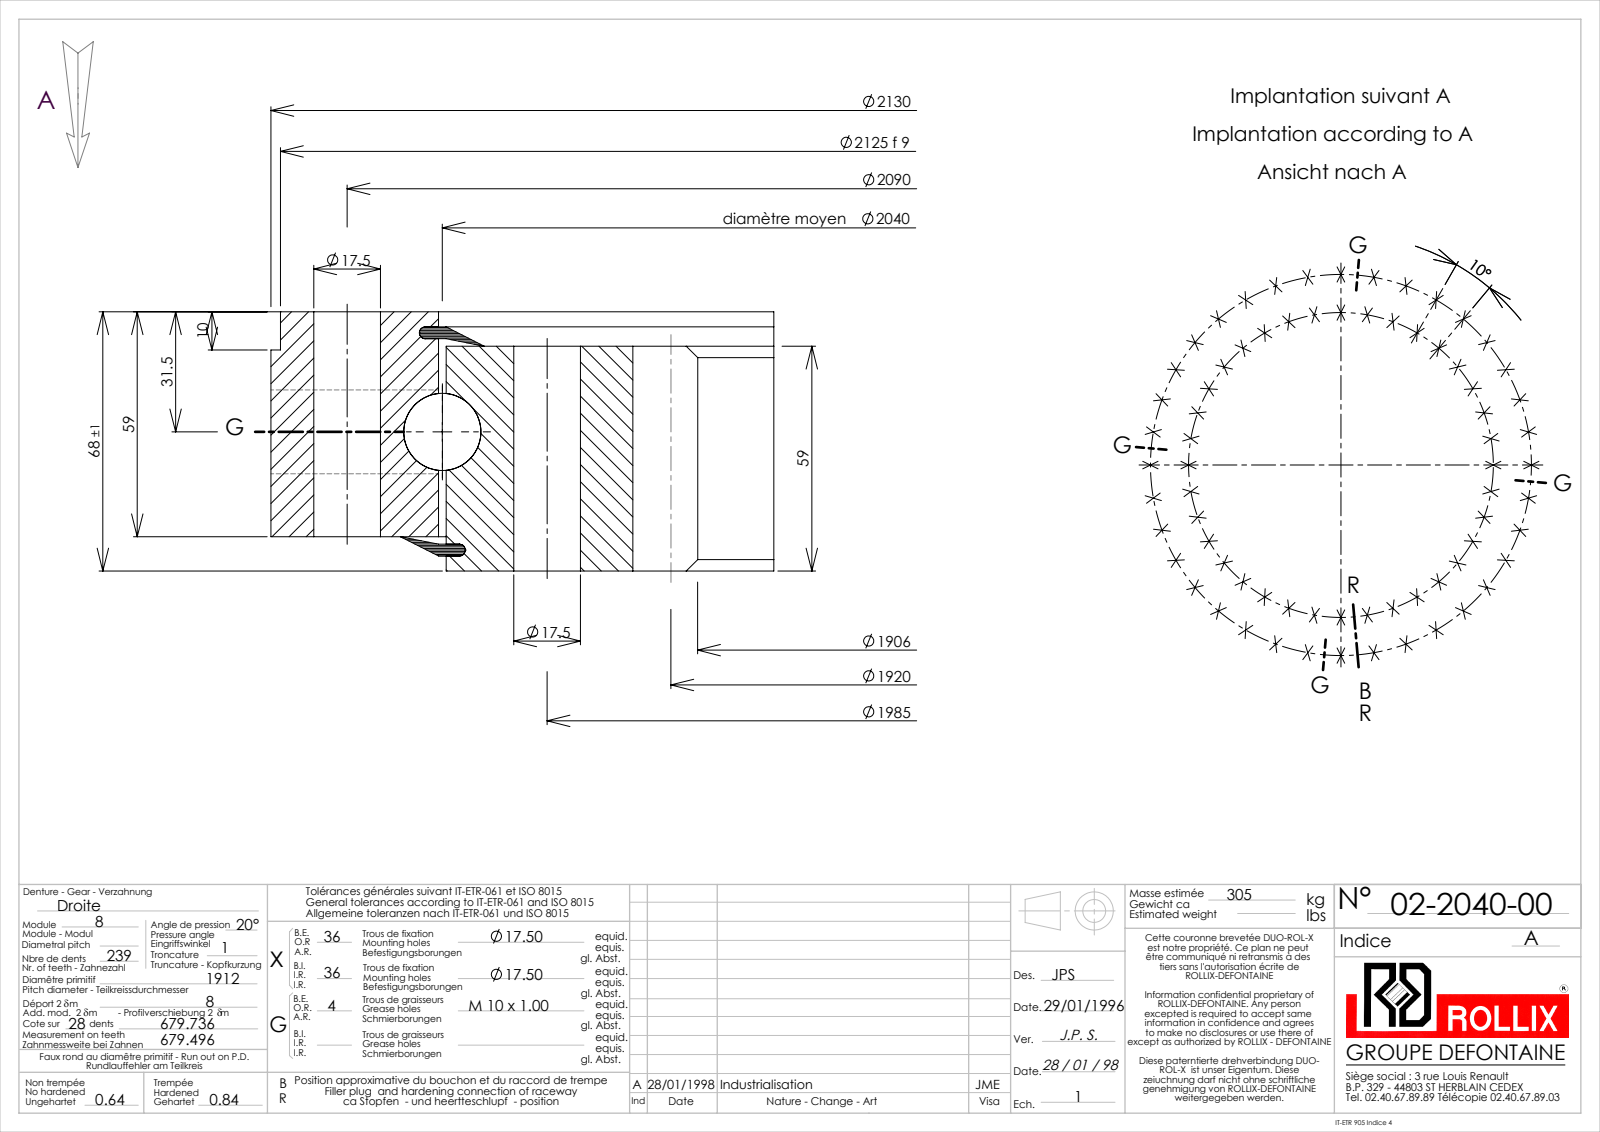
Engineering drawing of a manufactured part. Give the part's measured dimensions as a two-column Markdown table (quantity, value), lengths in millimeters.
| quantity | value |
| --- | --- |
| part name | 02-2040-00 |
| STEP written by | SolidWorks 2016 (CONFIG_CONTROL_DESIGN) |
| units | millimeters |
| bodies | 5 solids, 1649 faces (730 planar, 411 cylindrical, 508 other) |
| overall size | 2130 × 2130 × 68 |
| volume | 35 630 000 mm³ |
| surface area | 4 046 000 mm² |
| round holes (diameter × count) | 17.5 × 72, 9 × 4, 2042.03 × 1, 2052.03 × 1 |
| round bosses / shafts (diameter × count) | 2130 × 1, 2125 × 1, 2037.98 × 1, 2037.97 × 1, 2027.98 × 1 |
| partial cylindrical surfaces (radius × count) | 953 × 1 |
| main face-to-face distances | 59, 9, 50, 68, 7.05, 60.95, 1.95, 51.95, 3.95, 64.05 |
| hole center spacings | 1045, 362.92, 1712.03, 2058.25, 1477.85, 540.93, 1894.18, 1963.96 |
